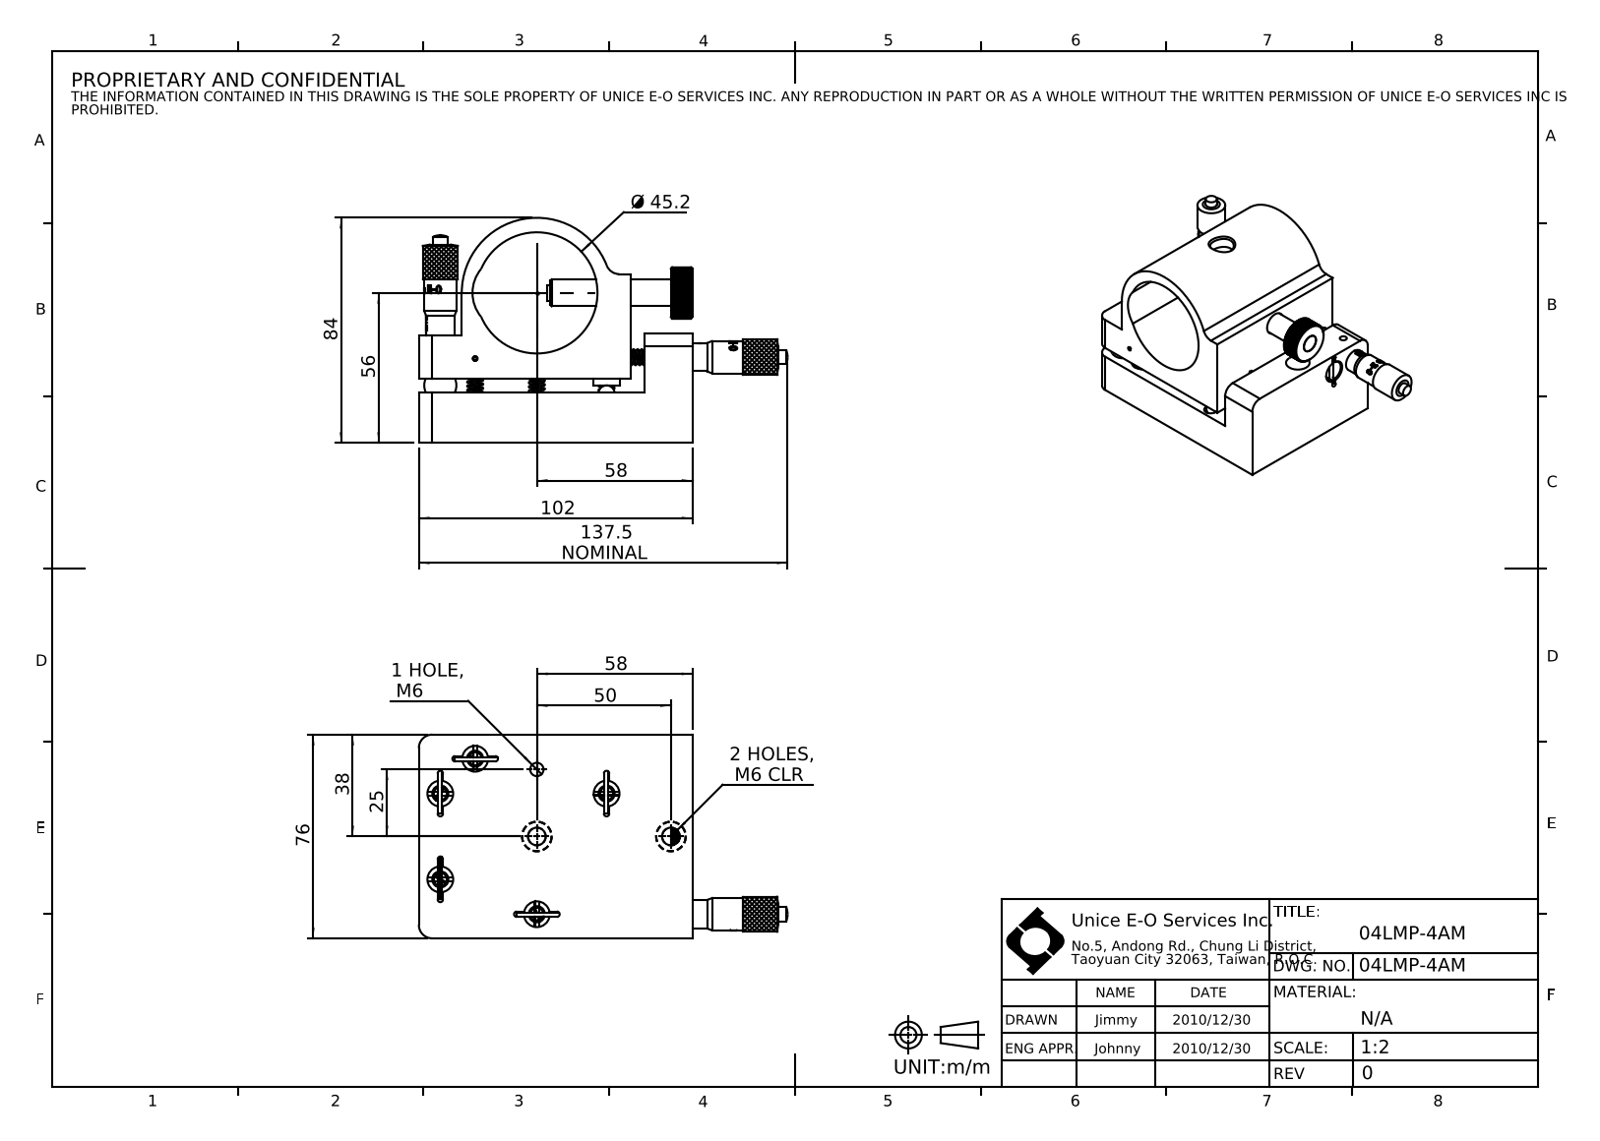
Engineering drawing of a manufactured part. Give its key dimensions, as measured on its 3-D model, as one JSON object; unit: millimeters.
{"part_name": "04LMP-4AM", "step_written_by": "SolidWorks 2016 (CONFIG_CONTROL_DESIGN)", "units": "millimeters", "bodies": {"solids": 31, "faces": 1390, "planar": 589, "cylindrical": 412, "other": 389}, "overall_size": [137.5, 84, 76], "volume_mm3": 316184, "surface_area_mm2": 86383, "round_holes": [[1.2, 10], [9.6, 6], [1.8, 5], [5, 3], [2.5, 2], [3.3, 2], [6.6, 2], [9.5, 2], [10.6, 2], [11, 2], [12.7, 2], [8, 1]], "round_bosses_or_shafts": [[1.6, 10], [0.6, 7], [6, 3], [13, 2], [12, 2], [10.5, 2], [9.9, 2], [9.2, 2]], "partial_cylinders_radius": [[0.1, 72], [1, 12], [5, 5], [3, 4], [5.98, 2], [9.5, 1], [14, 1], [28, 1]], "face_to_face_distances": [19, 5, 24, 76, 23, 16, 102, 79, 63, 17.9], "hole_center_spacings": [13, 4, 13.6, 25.61, 28.84, 32, 32.14, 33.8]}
